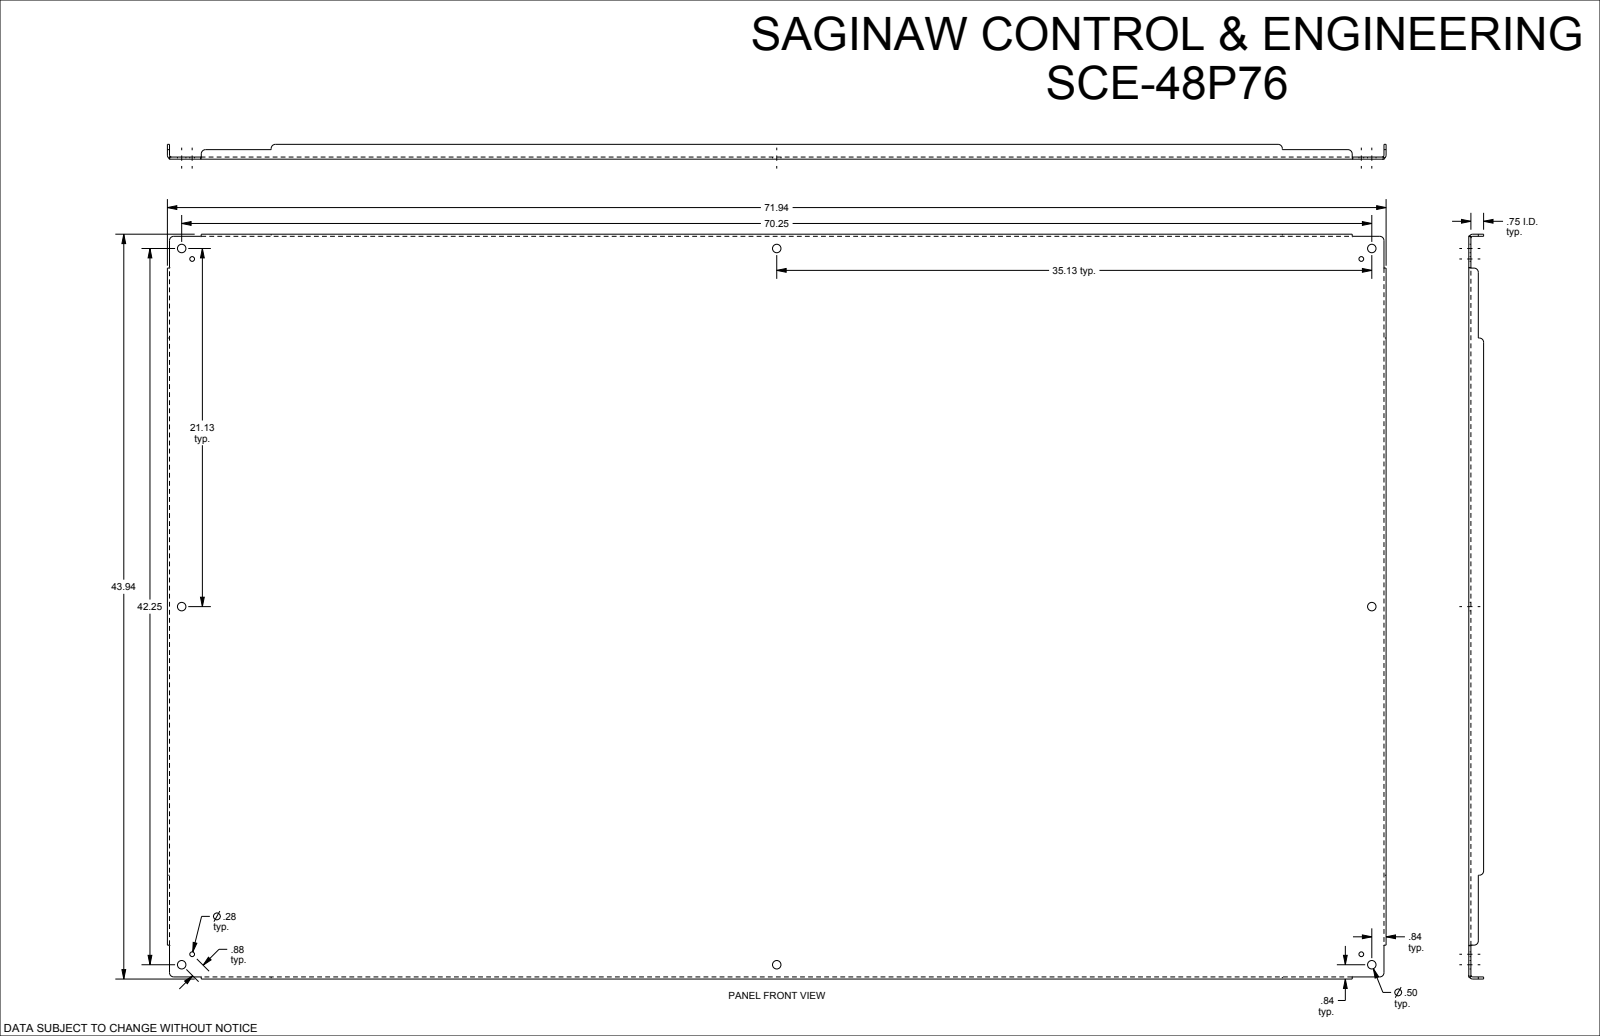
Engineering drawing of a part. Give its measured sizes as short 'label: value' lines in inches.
name: SCE-48P76
written by: SolidWorks 2019 (CONFIG_CONTROL_DESIGN)
unit: in
bodies: 1 solid, 110 faces (46 planar, 40 cylindrical, 24 other)
size: 71.938 × 43.938 × 0.875
volume: 411.5 in³; area: 6 616 in²
holes: 8× ⌀0.5, 4× ⌀0.281
rounds: 12× R0.25, 4× R0.112, 4× R0.237
face distances: 0.125, 0.125, 43.813, 71.813, 43.687, 43.938, 71.687, 71.938, 0.75, 0.875
hole spacings: 0.875, 20.516, 21.125, 34.512, 35.125, 40.988, 41.636, 54.072
